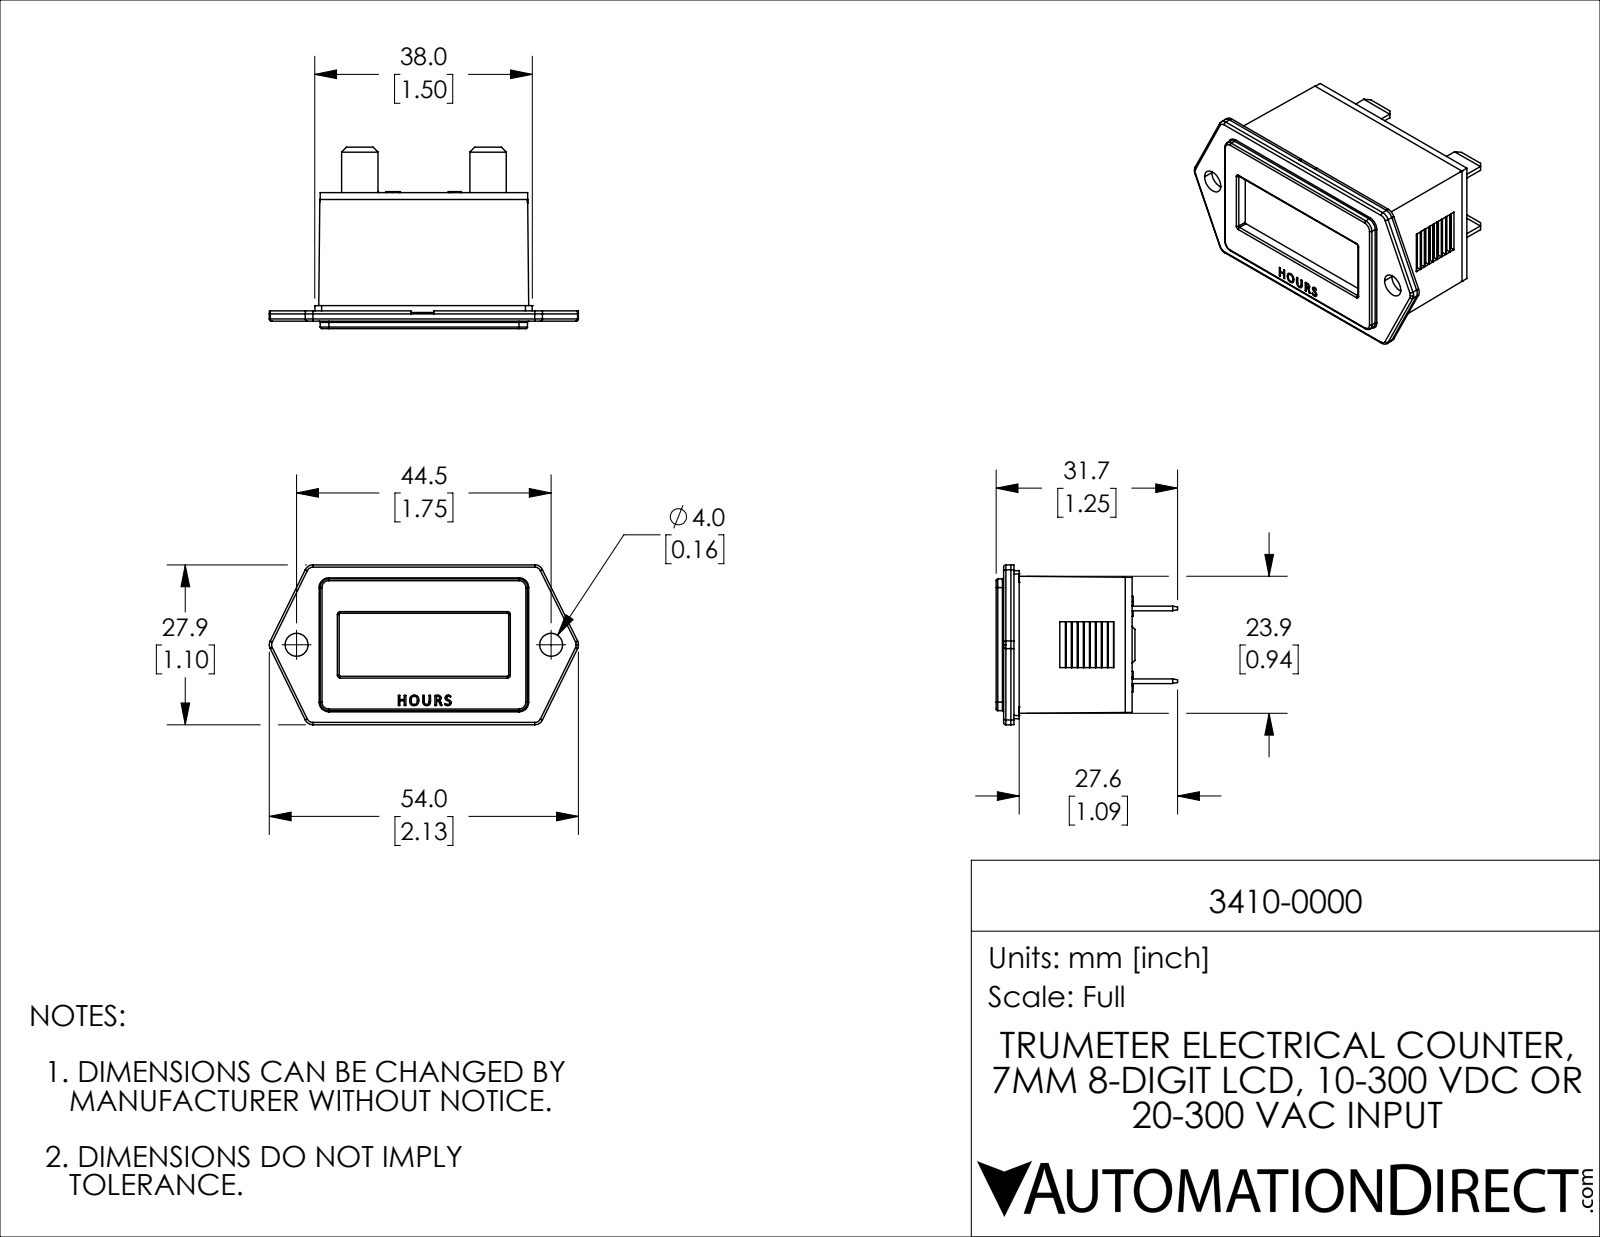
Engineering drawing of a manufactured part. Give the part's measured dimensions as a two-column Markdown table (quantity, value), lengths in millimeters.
| quantity | value |
| --- | --- |
| part name | 3410-0000 |
| STEP written by | SolidWorks 2021 (CONFIG_CONTROL_DESIGN) |
| units | millimeters |
| bodies | 2 solids, 618 faces (374 planar, 103 cylindrical, 141 other) |
| overall size | 53.98 × 31.68 × 27.9 |
| volume | 19 805 mm³ |
| surface area | 9 276 mm² |
| round holes (diameter × count) | 4 × 2 |
| partial cylindrical surfaces (radius × count) | 1.5 × 14, 0.2 × 8, 0.3 × 8, 0.25 × 6, 0.4 × 6, 0.76 × 4, 0.14 × 2, 0.25 × 2 |
| main face-to-face distances | 0.94, 20.9, 1.2, 21.84, 20.64, 20.61, 1.23, 19.67, 19.7, 0.8 |
| hole center spacings | 44.46 |
